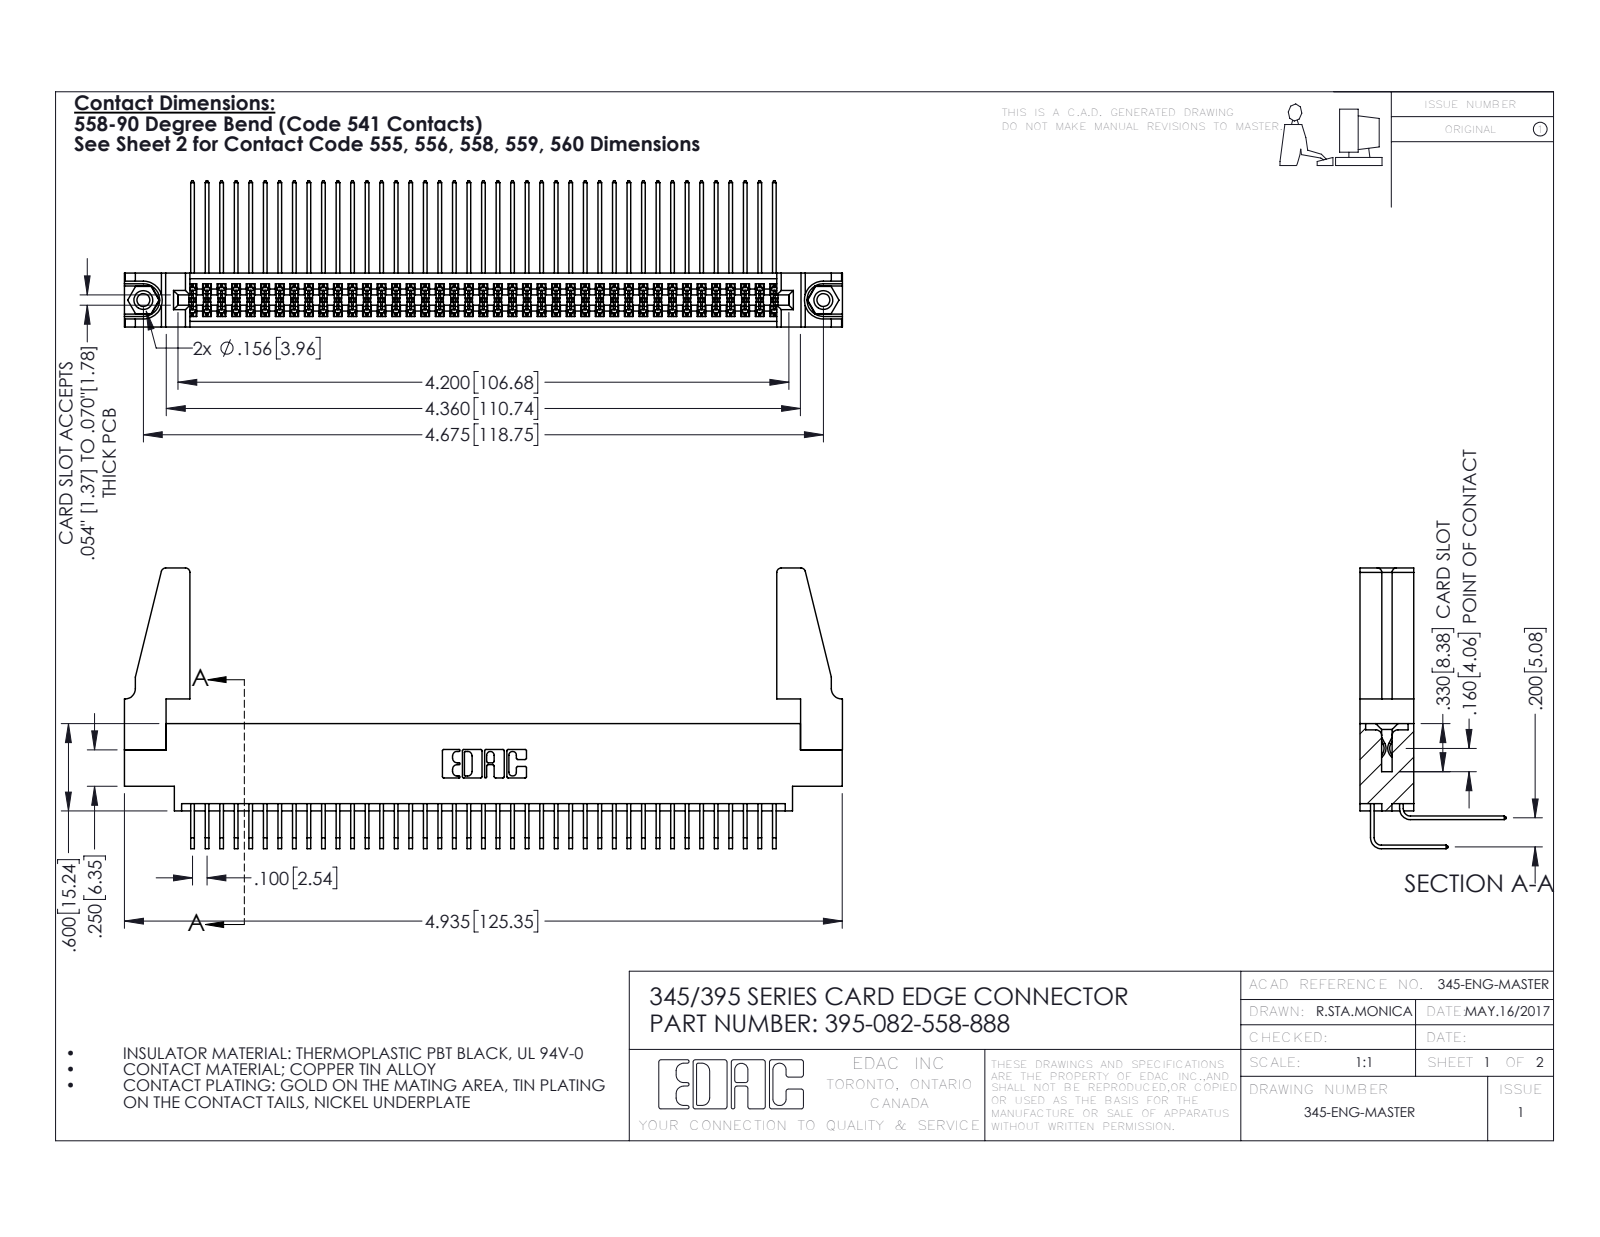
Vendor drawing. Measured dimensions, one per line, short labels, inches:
name: 345 Part_0.170 Offset - 0.156 Dia-TH; 345-220-078_345-220-088; 345-292-001_558 Tail - 2; 345-292-001_558 559 Tail - 1 (+2 more)
written by: SolidWorks 2016 (CONFIG_CONTROL_DESIGN)
unit: in
bodies: 87 solids, 4518 faces (3026 planar, 1476 cylindrical, 16 other)
size: 4.936 × 1.929 × 1.005
volume: 0.963 in³; area: 37.19 in²
holes: 2× ⌀0.089, 2× ⌀0.125, 2× ⌀0.156, 1× ⌀0.064
bosses: 2× ⌀0.155
rounds: 124× R0.006, 22× R0.01, 8× R0.03, 6× R0.007, 6× R0.031, 3× R0.026, 2× R0.014, 2× R0.019
face distances: 0.072, 0.298, 0.37, 0.2, 0.098, 0.272, 0.025, 0.225, 0.175, 0.025
hole spacings: 0.27, 4.439, 4.675
